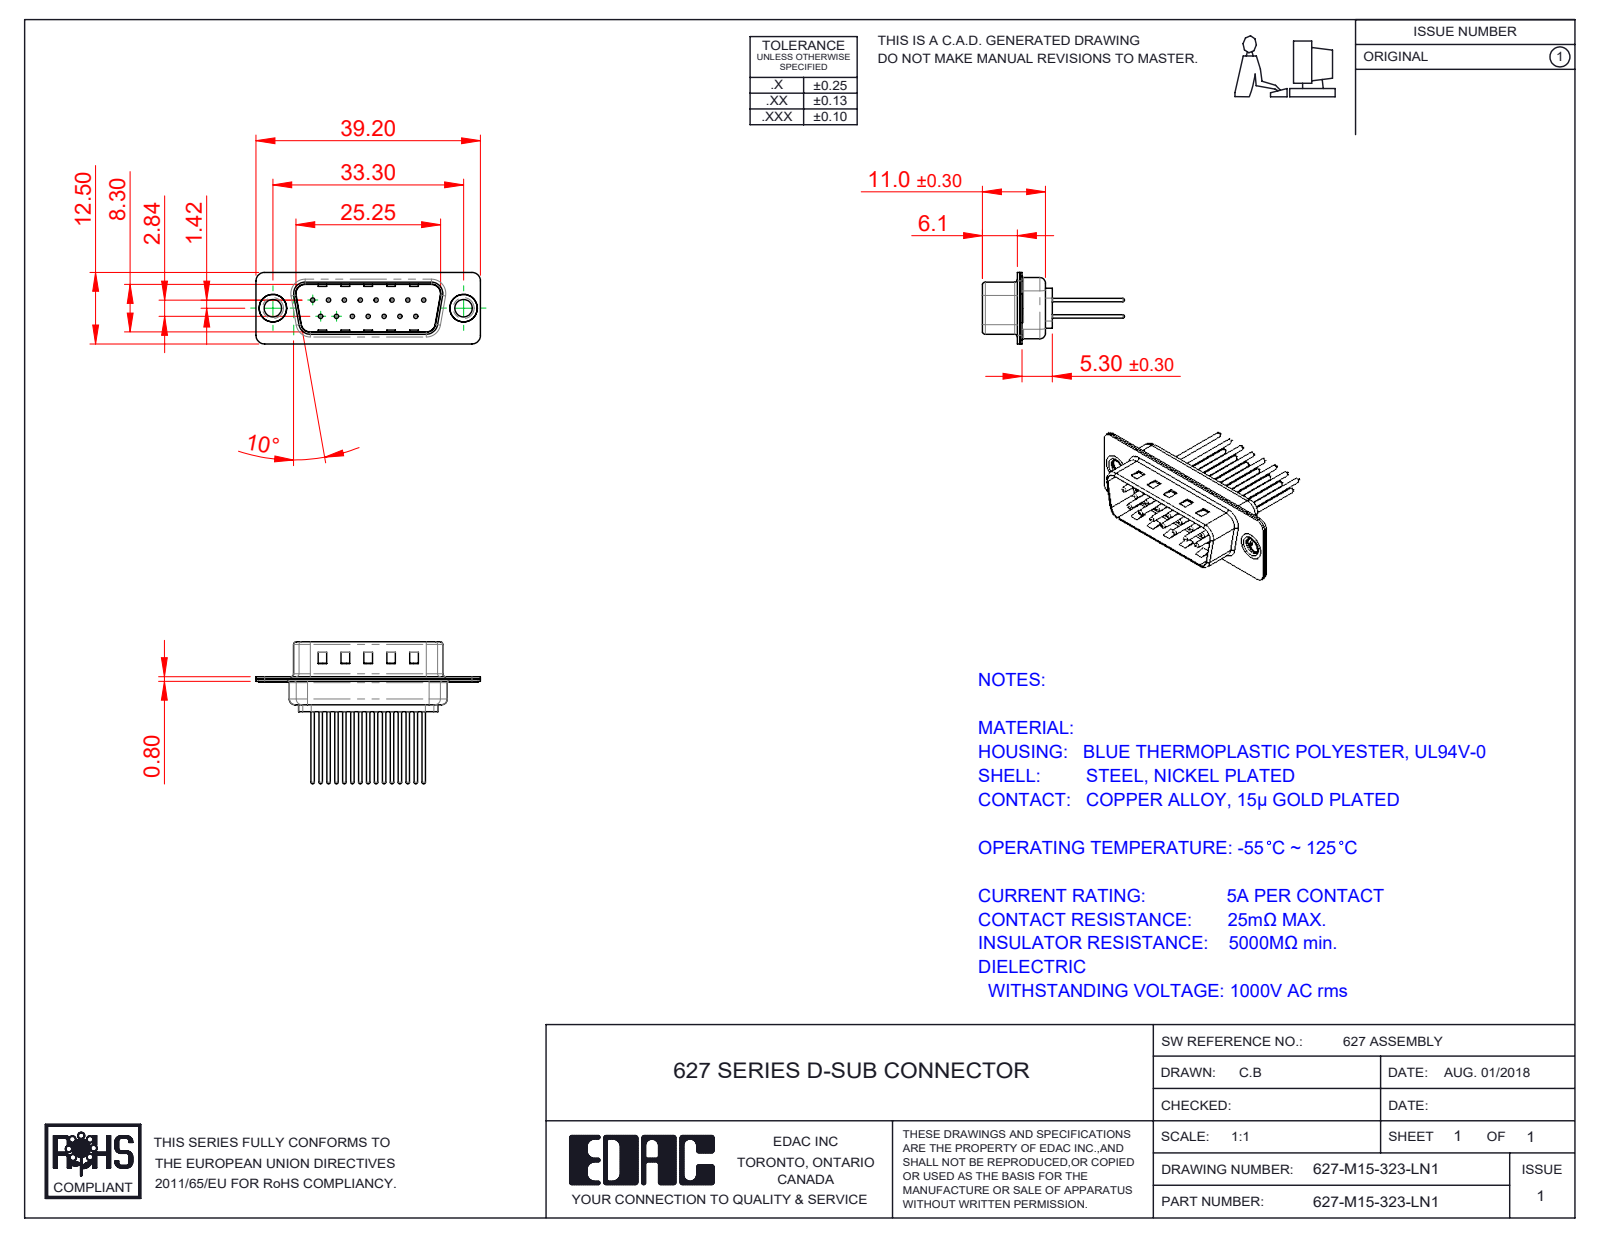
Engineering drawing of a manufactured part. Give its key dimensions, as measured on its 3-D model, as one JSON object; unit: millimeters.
{"part_name": "627M Contact Row 1_23; 627-M15-323-LN1; 627M Housing_15 Contacts; 627M Contact Row 2_23 (+3 more)", "step_written_by": "SolidWorks 2020 (CONFIG_CONTROL_DESIGN)", "units": "millimeters", "bodies": {"solids": 20, "faces": 869, "planar": 244, "cylindrical": 327, "other": 298}, "overall_size": [39.2, 24.77, 12.5], "volume_mm3": 1794, "surface_area_mm2": 4857, "round_holes": [[0.75, 15], [1.6, 15], [2, 15], [3.05, 2], [4, 2], [4.8, 2]], "round_bosses_or_shafts": [[1.5, 15], [0.6, 15], [5, 2], [4.9, 2], [3.55, 2]], "partial_cylinders_radius": [[1.5, 16], [2, 12], [0.5, 8], [1.6, 8], [0.25, 4], [0.6, 4], [0.65, 4], [0.9, 4]], "face_to_face_distances": [0.4, 0.8, 9.5, 9.1, 8.7, 9.9, 1.2, 6.1, 5.3, 5.7], "hole_center_spacings": [3.16, 2.77, 5.54, 8.31, 11.08, 5.03, 5.04, 7.48]}
